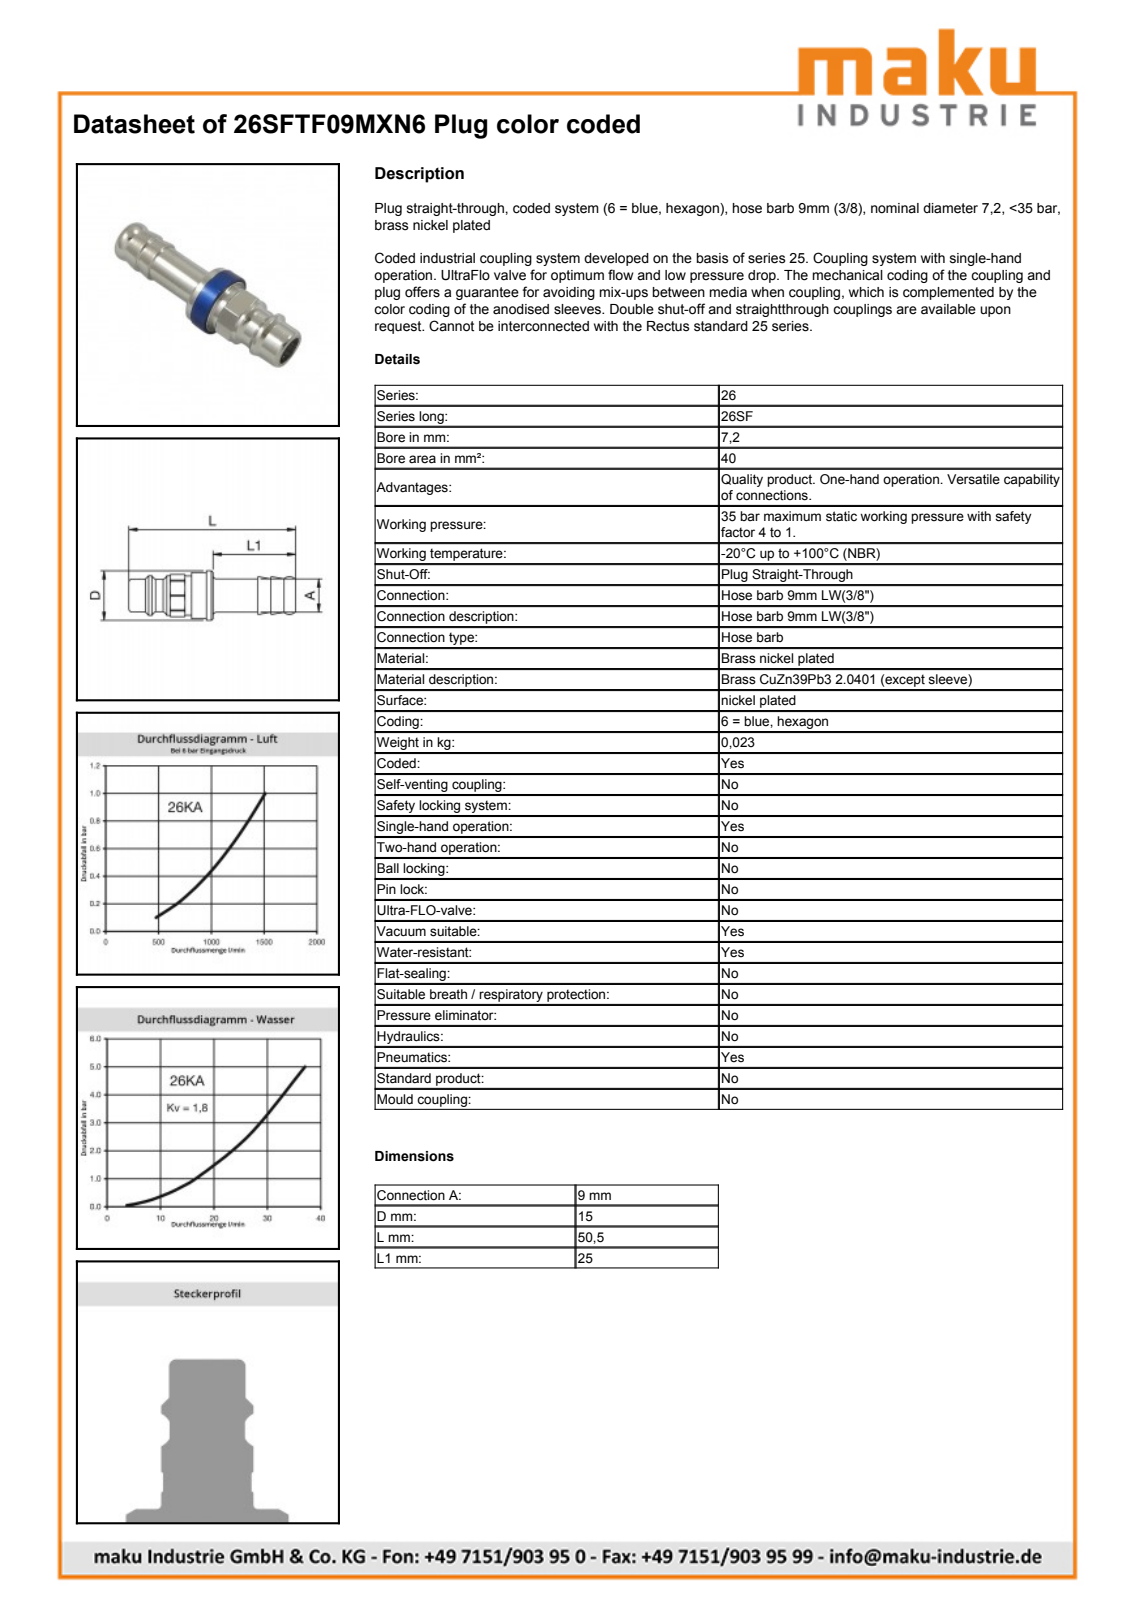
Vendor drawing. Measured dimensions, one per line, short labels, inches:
name: D106593; D106532; D103012
written by: Autodesk Inventor 2011 (AUTOMOTIVE_DESIGN)
unit: in
bodies: 2 solids, 61 faces (14 planar, 18 cylindrical, 29 other)
size: 1.988 × 0.61 × 0.61
volume: 0.175 in³; area: 5.524 in²
holes: 1× ⌀0.276, 1× ⌀0.545, 1× ⌀0.553
bosses: 1× ⌀0.61, 1× ⌀0.591, 1× ⌀0.551, 1× ⌀0.472, 1× ⌀0.469, 1× ⌀0.394, 1× ⌀0.384, 1× ⌀0.358
rounds: 1× R0.268
face distances: 0.472, 0.079, 0.256, 0.177, 0.244, 0.165, 0.984, 1.063, 1.228, 1.24
